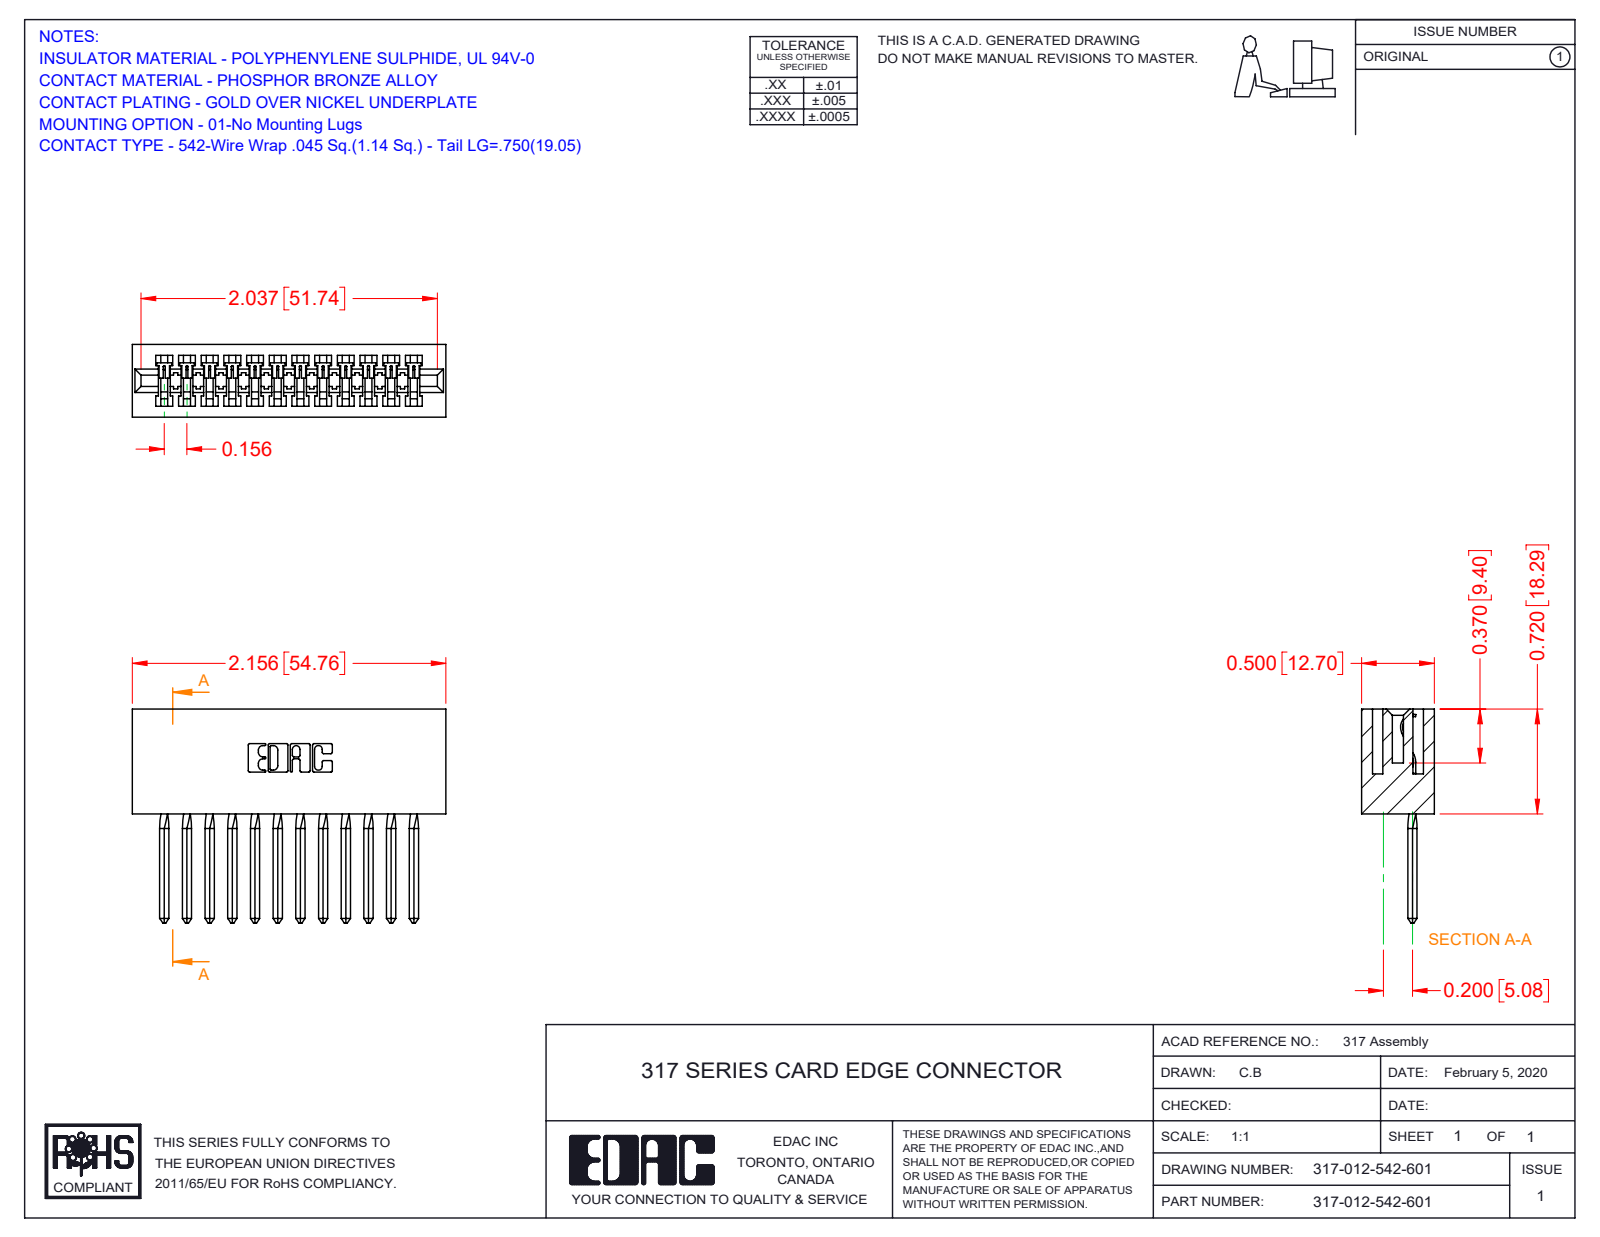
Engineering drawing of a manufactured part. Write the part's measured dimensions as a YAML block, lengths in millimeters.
part_name: "317 Part_Lugless; 317-012-542-601; 317-290-003_542"
step_written_by: "SolidWorks 2016 (CONFIG_CONTROL_DESIGN)"
units: millimeters
bodies: {solids: 13, faces: 990, planar: 818, cylindrical: 124, other: 48}
overall_size: [54.8, 37.3, 12.7]
volume: 9240
surface_area: 10650
partial_cylinders:
  - {radius: 0.2, count: 24}
  - {radius: 0.3, count: 22}
  - {radius: 0.2, count: 6}
  - {radius: 0.8, count: 6}
  - {radius: 0.7, count: 3}
  - {radius: 1.9, count: 1}
  - {radius: 2.3, count: 1}
  - {radius: 2.5, count: 1}
face_to_face_distances: [12.7, 1.9, 10.8, 2.8, 1.7, 4, 8.9, 5.6, 2.9, 3.5]
